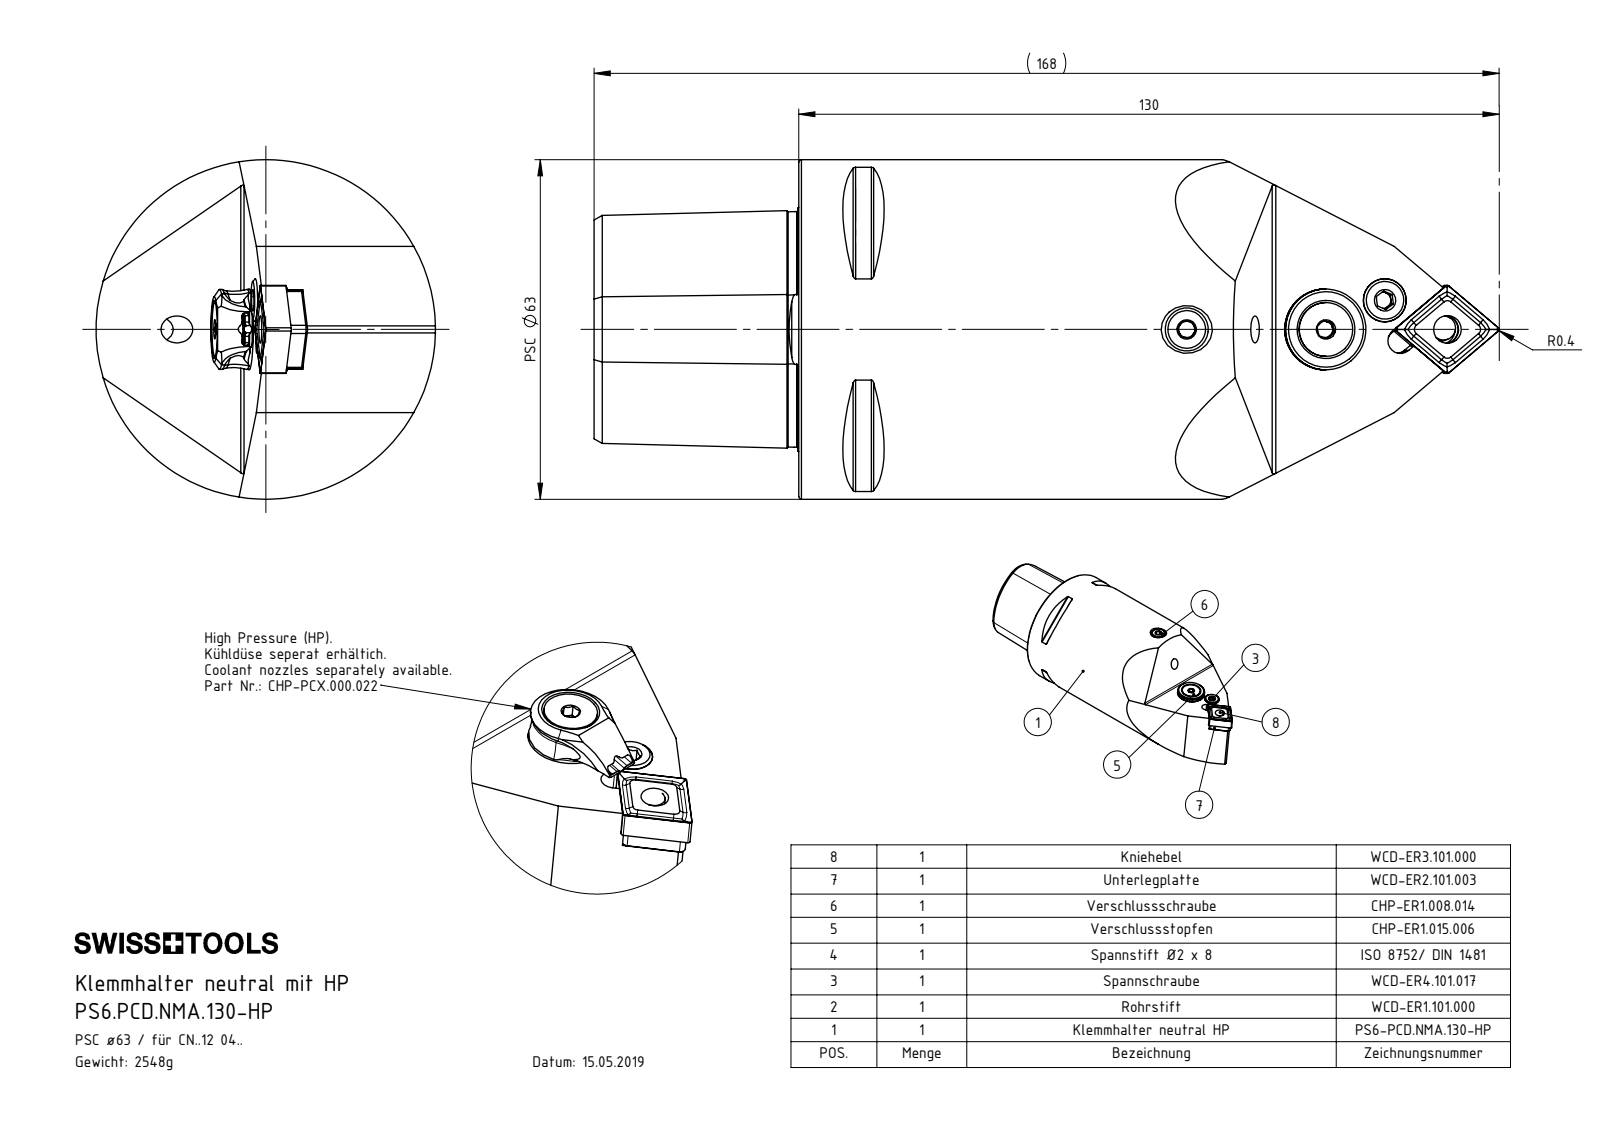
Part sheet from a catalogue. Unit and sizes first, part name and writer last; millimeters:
Units: millimetres
Overall size (bounding box): 168 × 63 × 63
Round holes (diameter × count): ⌀4.2 ×2, ⌀5 ×2, ⌀7 ×2, ⌀1.2 ×1, ⌀2 ×1, ⌀2.5 ×1, ⌀3 ×1, ⌀4 ×1, ⌀5.16 ×1, ⌀5.2 ×1, ⌀6.4 ×1, ⌀8.1 ×1
Round bosses / shafts (diameter × count): ⌀8 ×2, ⌀63 ×1, ⌀15 ×1, ⌀13.4 ×1, ⌀10 ×1, ⌀7.9 ×1, ⌀6.4 ×1, ⌀5.5 ×1
Partial cylindrical surfaces — rounded edges, fillets, slot ends (radius × count): R0.5 ×10, R0.4 ×4, R1 ×4, R2.5 ×3, R2.1 ×1, R2.2 ×1, R2.35 ×1, R2.8 ×1
Main face-to-face distances: 38, 26.82, 24.88, 4.5, 27, 11, 4.45, 11.79, 55.8, 3.13
Hole centre spacings: 4.51, 4.49, 4.53, 12.24, 12.25, 12.8, 12.85, 16.75
Volume: 331 416 mm³ · Surface area: 44 956 mm²
Bodies: 11 solids, 448 faces (134 planar, 116 cylindrical, 198 other)
Part name (STEP PRODUCT): WCD-ER2.101.003_A; ISO 8752 2x8; DIN 3771 - 13x1; WCD-ER1.101.000 (+8 more)
STEP written by: SolidWorks 2017 (AUTOMOTIVE_DESIGN)
